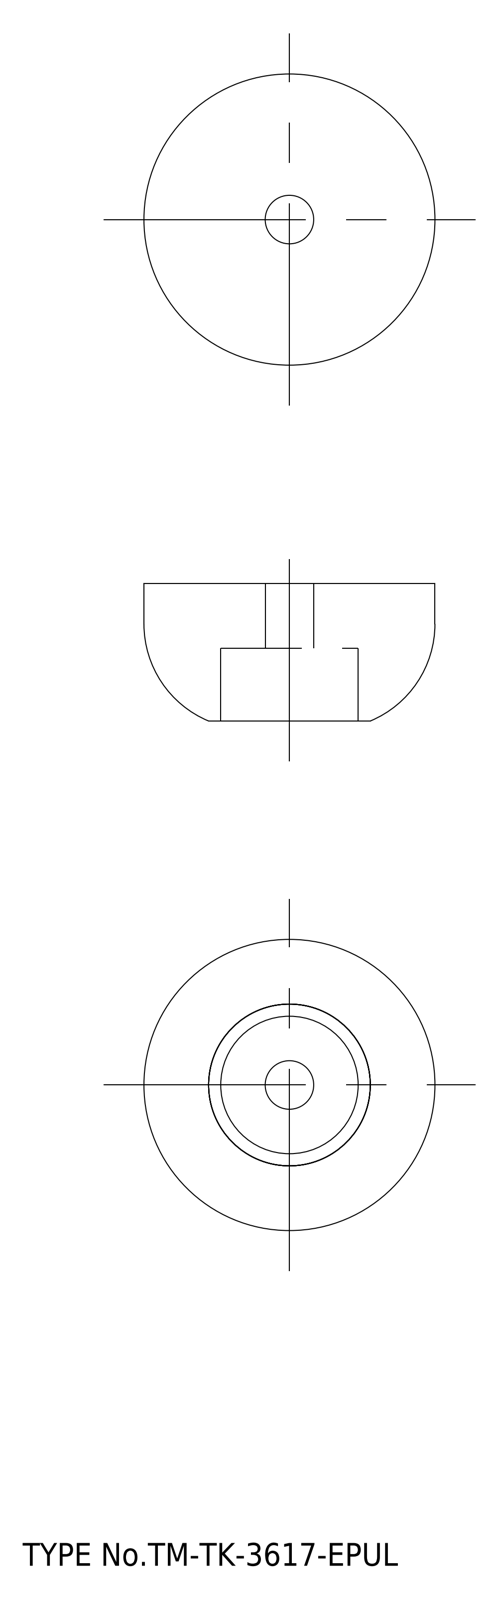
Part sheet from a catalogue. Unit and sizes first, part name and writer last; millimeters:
Units: millimetres
Overall size (bounding box): 36 × 36 × 17
Round holes (diameter × count): ⌀6 ×1, ⌀17 ×1, ⌀18 ×1
Round bosses / shafts (diameter × count): ⌀36 ×1
Main face-to-face distances: 7, 1, 8, 9, 10, 17
Volume: 12 389 mm³ · Surface area: 4 554 mm²
Bodies: 2 solids, 20 faces (6 planar, 12 cylindrical, 2 other)
Part name (STEP PRODUCT): washer; rubber foot
STEP written by: spGate 15.6.1 (AUTOMOTIVE_DESIGN)
